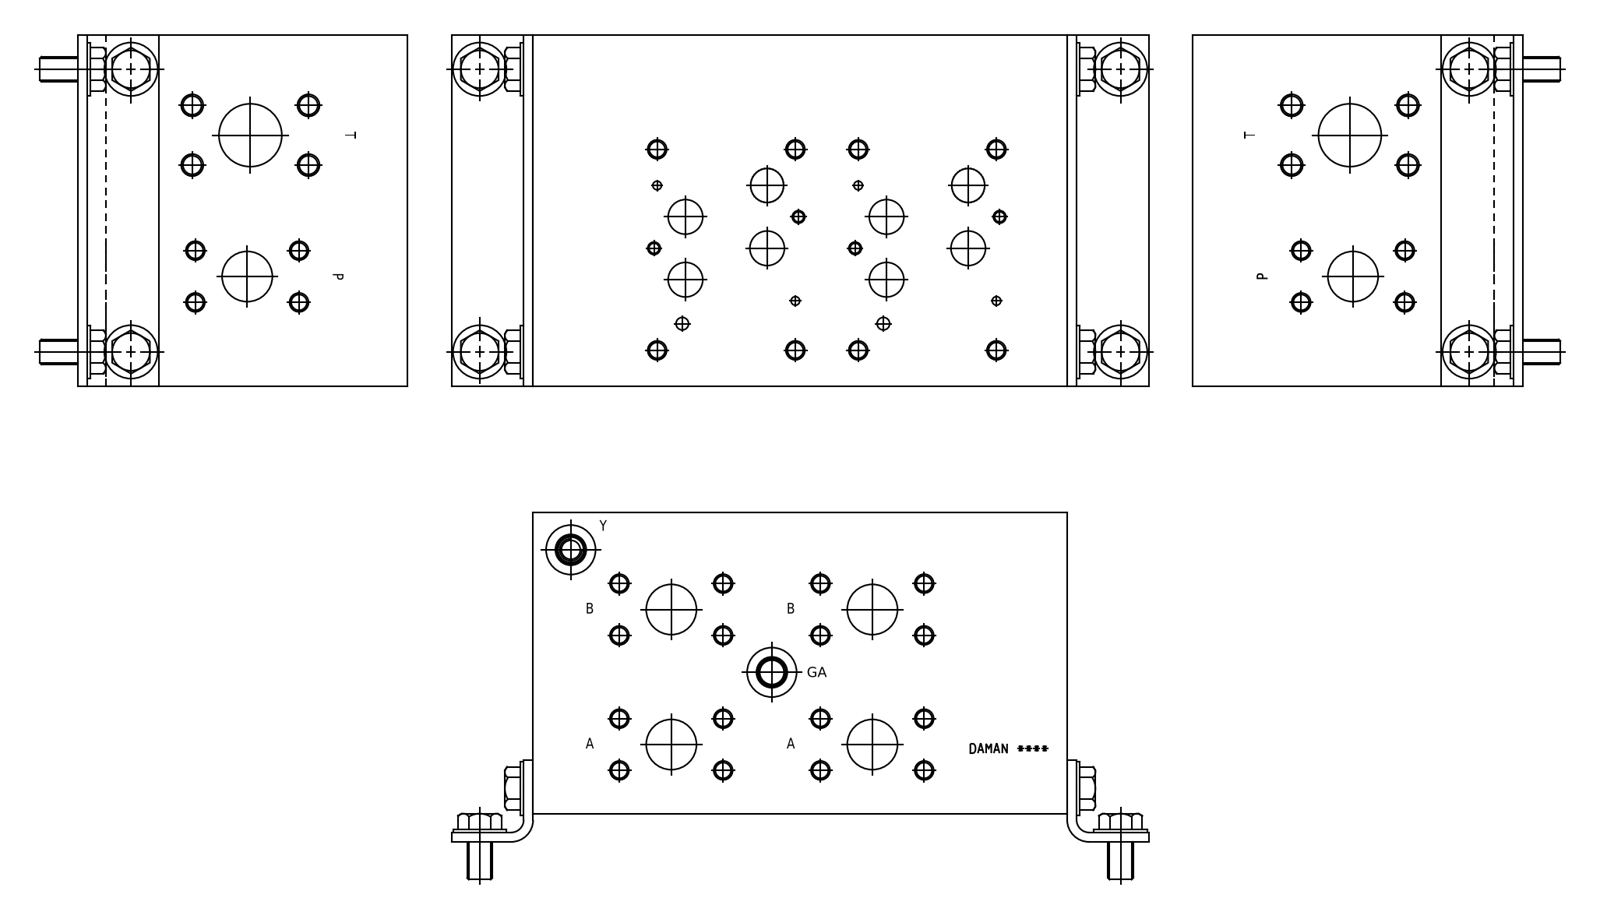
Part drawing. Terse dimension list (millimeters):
name: Part_AD07HP024F_3D
written by: Autodesk Inventor 2020 (AUTOMOTIVE_DESIGN)
unit: mm
bodies: 1 solid, 733 faces (410 planar, 128 cylindrical, 195 other)
size: 269.88 × 177.8 × 152.4
volume: 7 137 000 mm³; area: 286 063 mm²
holes: 31× ⌀9.53, 30× ⌀7.92, 6× ⌀6.35, 6× ⌀9.35, 6× ⌀11.13, 6× ⌀17.48, 5× ⌀25.4, 4× ⌀4.37, 4× ⌀5.11, 2× ⌀10.72, 2× ⌀12.7, 2× ⌀14.27
face distances: 152.4, 177.8, 269.88, 25.4, 0.79, 177.01, 24.61, 25.36, 3.05, 28.45
hole spacings: 101.6, 26.17, 29.27, 29.28, 52.38, 58.55, 68.25, 122.4
